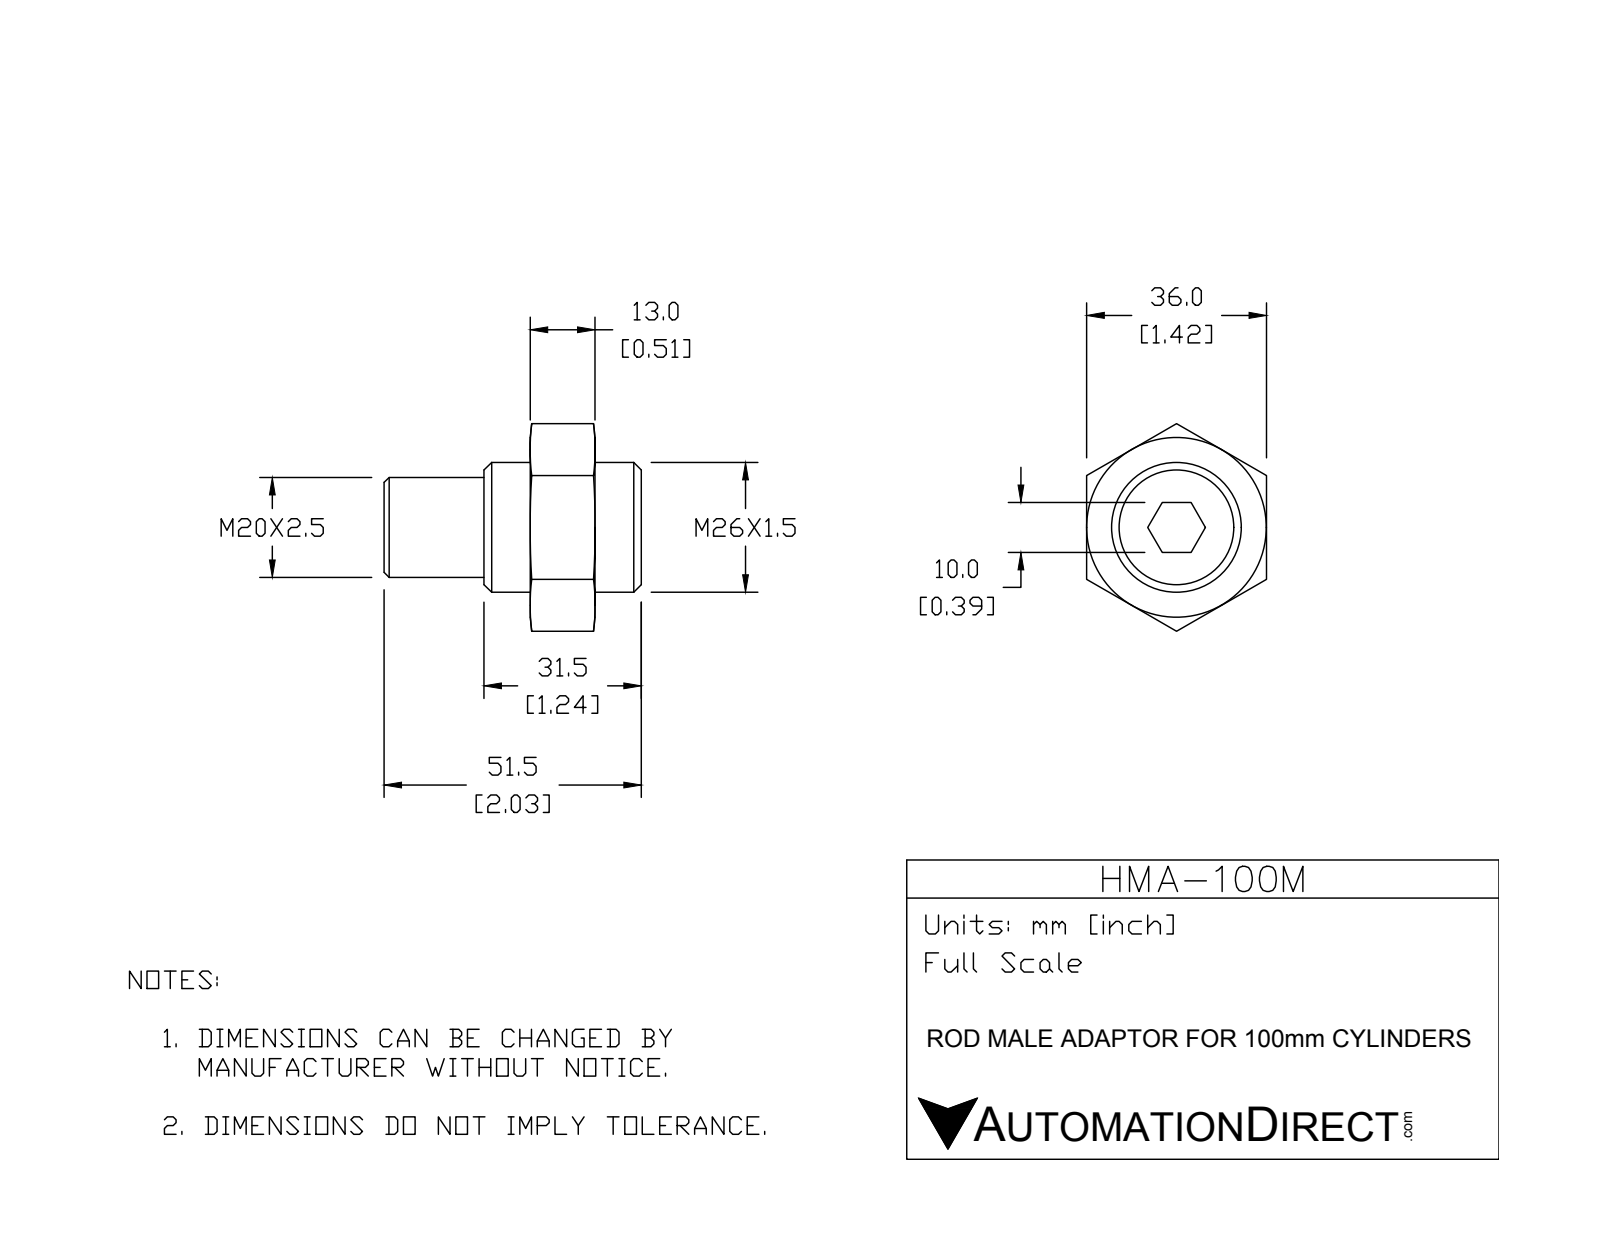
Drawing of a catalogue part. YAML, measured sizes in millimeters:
part_name: "HMA-100M"
step_written_by: "SolidWorks 2015 (CONFIG_CONTROL_DESIGN)"
units: millimeters
bodies: {solids: 2, faces: 44, planar: 18, cylindrical: 6, other: 20}
overall_size: [51.5, 41.57, 36]
volume: 29683
surface_area: 8854
round_holes:
  - {diameter: 26, count: 1}
round_bosses_or_shafts:
  - {diameter: 20, count: 1}
face_to_face_distances: [36, 13, 9.25, 22.25, 51.5, 42.25, 29.25, 10, 31.5, 20]
